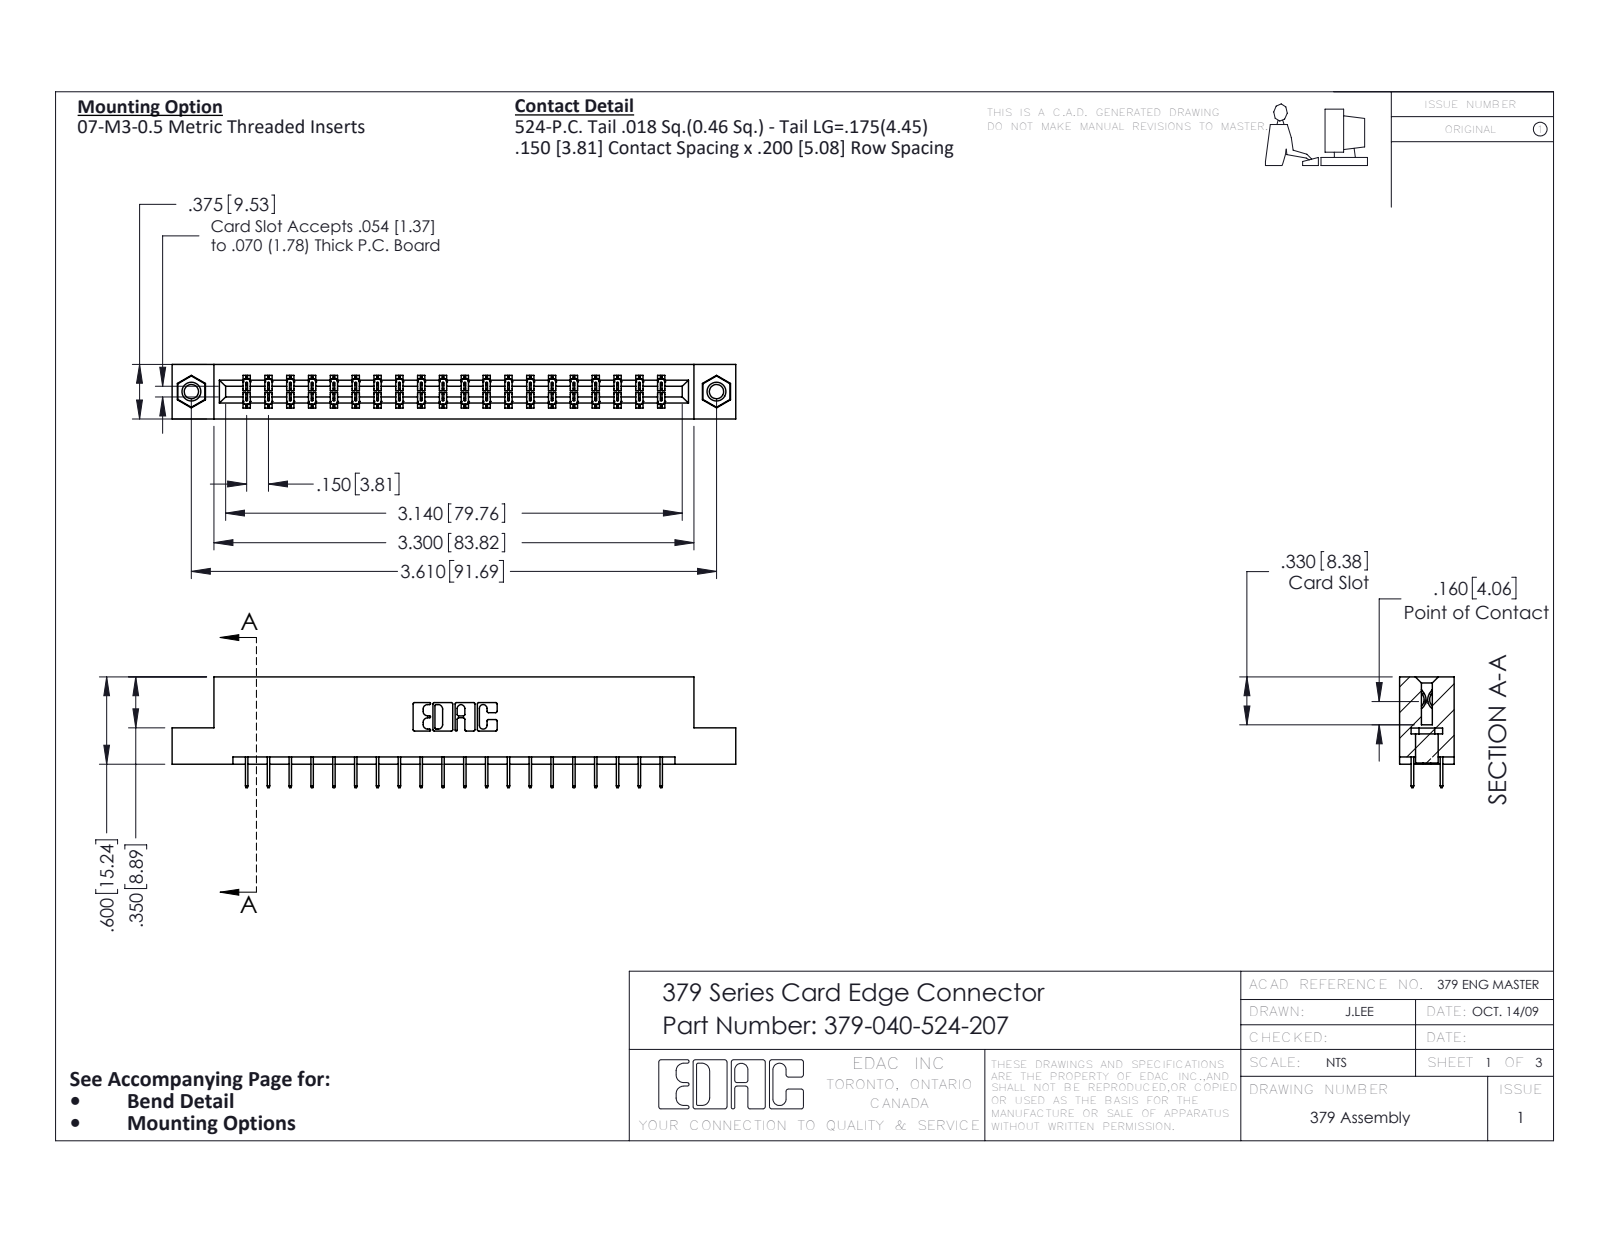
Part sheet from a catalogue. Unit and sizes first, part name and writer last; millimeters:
Units: millimetres
Overall size (bounding box): 98.4 × 19.4 × 9.5
Round holes (diameter × count): ⌀2.5 ×2, ⌀3.2 ×2, ⌀4 ×2
Round bosses / shafts (diameter × count): ⌀3.9 ×2
Partial cylindrical surfaces — rounded edges, fillets, slot ends (radius × count): R0.2 ×60, R0.3 ×22, R0.2 ×6, R0.8 ×6, R0.7 ×3, R0.4 ×2, R0.6 ×2, R0.6 ×2
Main face-to-face distances: 7.6, 9.5, 1.9, 5.1, 2.5, 5.7, 3.8, 1.3, 15.2, 14
Hole centre spacings: 91.7
Volume: 10 100 mm³ · Surface area: 11 030 mm²
Bodies: 43 solids, 2414 faces (1782 planar, 616 cylindrical, 16 other)
Part name (STEP PRODUCT): 379-040-524-207; 345-250-001_345-250-005-103; 379 Part_Flush - .156 Dia - TI; 345-292-001_345-293-124
STEP written by: SolidWorks 2016 (CONFIG_CONTROL_DESIGN)
